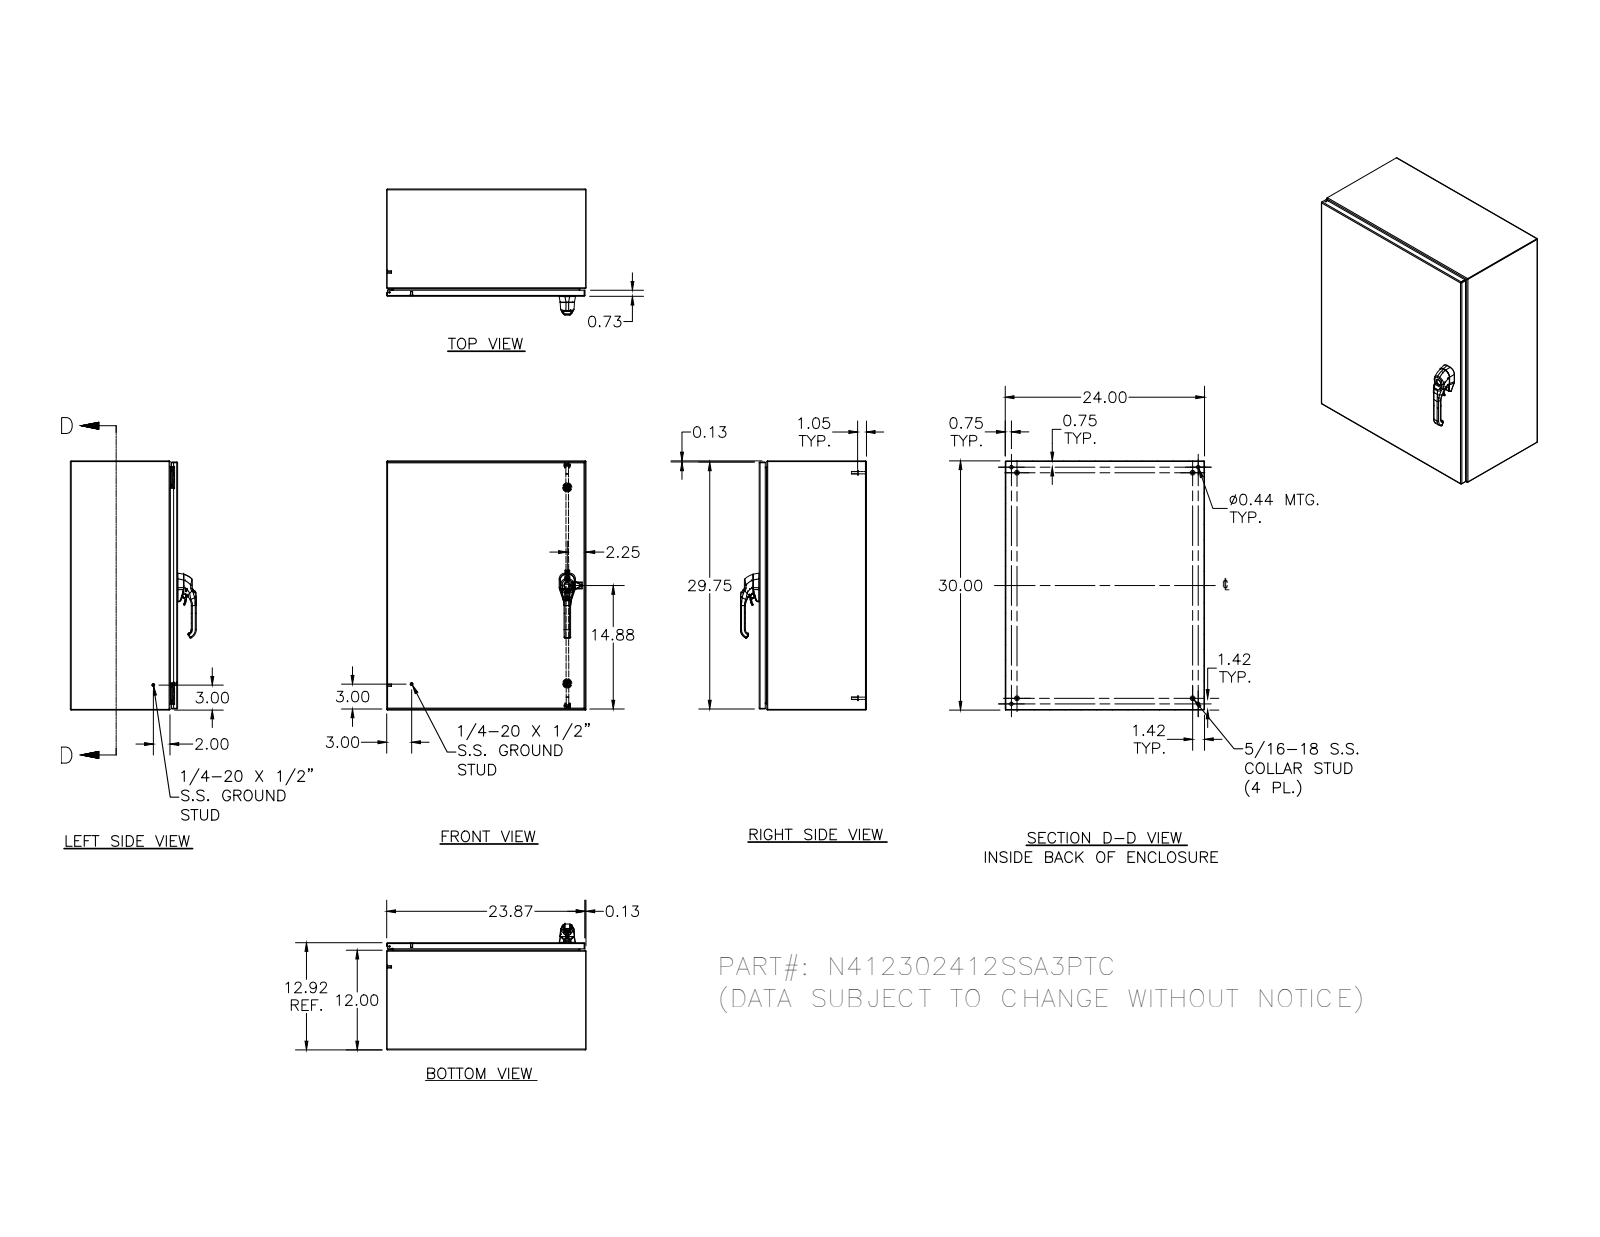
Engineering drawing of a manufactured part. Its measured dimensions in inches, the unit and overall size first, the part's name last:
Units: inches
Overall size (bounding box): 30 × 24 × 15.166
Round holes (diameter × count): ⌀0.165 ×5, ⌀0.188 ×5, ⌀0.093 ×4, ⌀0.152 ×4, ⌀0.167 ×4, ⌀0.172 ×4, ⌀0.197 ×4, ⌀0.437 ×4, ⌀0.213 ×3, ⌀0.106 ×2, ⌀0.156 ×2, ⌀0.16 ×2
Round bosses / shafts (diameter × count): ⌀0.25 ×10, ⌀0.236 ×6, ⌀0.591 ×4, ⌀0.563 ×4, ⌀0.36 ×4, ⌀0.32 ×4, ⌀0.31 ×4, ⌀0.3 ×4
Partial cylindrical surfaces — rounded edges, fillets, slot ends (radius × count): R0.02 ×180, R0.012 ×101, R0.031 ×30, R0.05 ×26, R0.118 ×23, R0.019 ×21, R0.105 ×20, R0.016 ×18
Main face-to-face distances: 0.074, 12.843, 23.926, 12.917, 12.769, 29.926, 23.852, 24, 30, 29.852
Hole centre spacings: 25.996, 22.869, 0.017, 0.66, 1.618, 26.656, 0.019, 0.5
Volume: 229.1 in³ · Surface area: 6 067 in²
Bodies: 63 solids, 3088 faces (1046 planar, 1119 cylindrical, 923 other)
Part name (STEP PRODUCT): N412302412SSA3PTC; N412302412SSA3PTCBKP; N4123024SSA3PTCLID; HFW328176 (+8 more)
STEP written by: Autodesk Inventor 2011 (AUTOMOTIVE_DESIGN)
